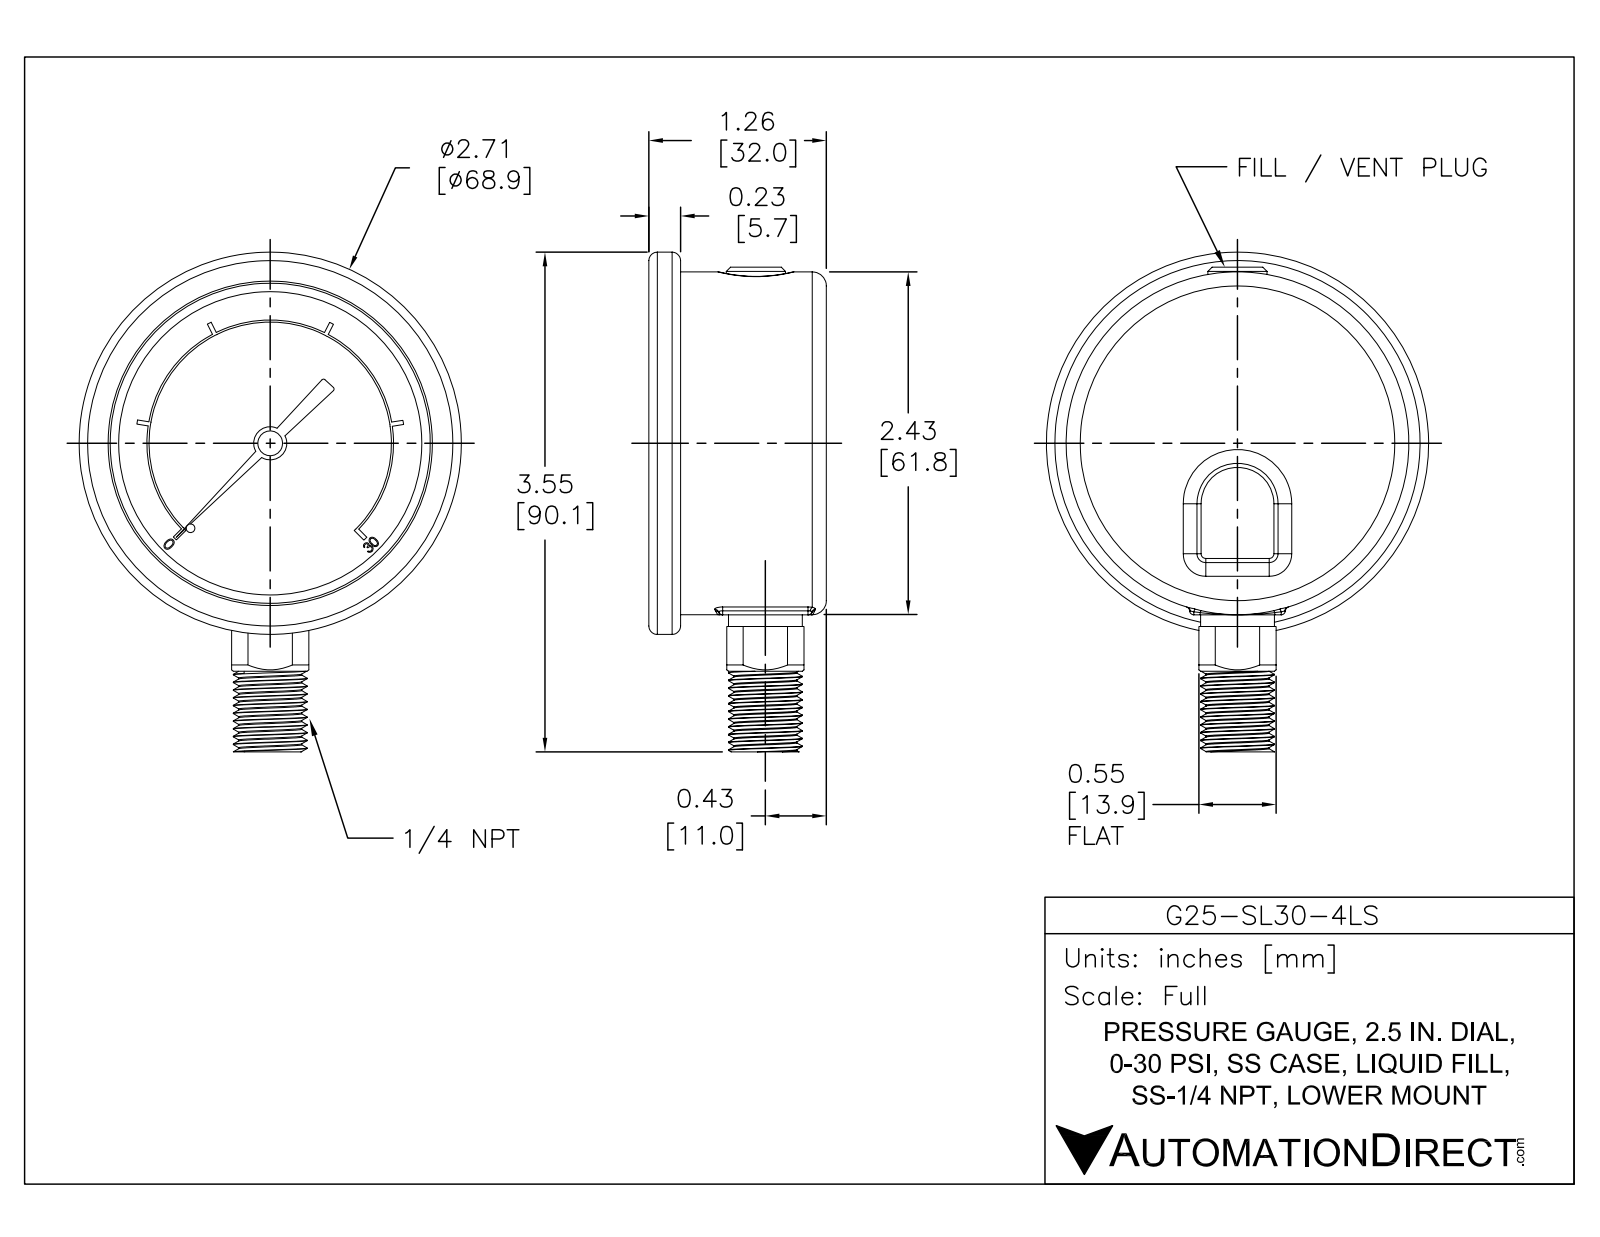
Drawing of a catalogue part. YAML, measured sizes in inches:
part_name: "G25-SL30-4LS"
step_written_by: "SolidWorks 2021 (AUTOMOTIVE_DESIGN)"
units: inches
bodies: {solids: 1, faces: 343, planar: 190, cylindrical: 85, other: 68}
overall_size: [3.546, 2.713, 1.26]
volume: 5.273
surface_area: 24.68
round_holes:
  - {diameter: 0.027, count: 1}
  - {diameter: 0.071, count: 1}
  - {diameter: 0.119, count: 1}
  - {diameter: 2.272, count: 1}
round_bosses_or_shafts:
  - {diameter: 2.713, count: 1}
  - {diameter: 2.433, count: 1}
  - {diameter: 0.524, count: 1}
  - {diameter: 0.42, count: 1}
  - {diameter: 0.235, count: 1}
  - {diameter: 0.176, count: 1}
  - {diameter: 0.14, count: 1}
  - {diameter: 0.041, count: 1}
partial_cylinders:
  - {radius: 0.03, count: 9}
  - {radius: 0.1, count: 3}
  - {radius: 0.015, count: 2}
  - {radius: 0.316, count: 1}
  - {radius: 0.86, count: 1}
  - {radius: 0.875, count: 1}
face_to_face_distances: [1.01, 1.26, 0.25, 1.035, 0.025, 0.225, 0.1, 0.91, 0.935, 1.16]
hole_center_spacings: [0.067]
